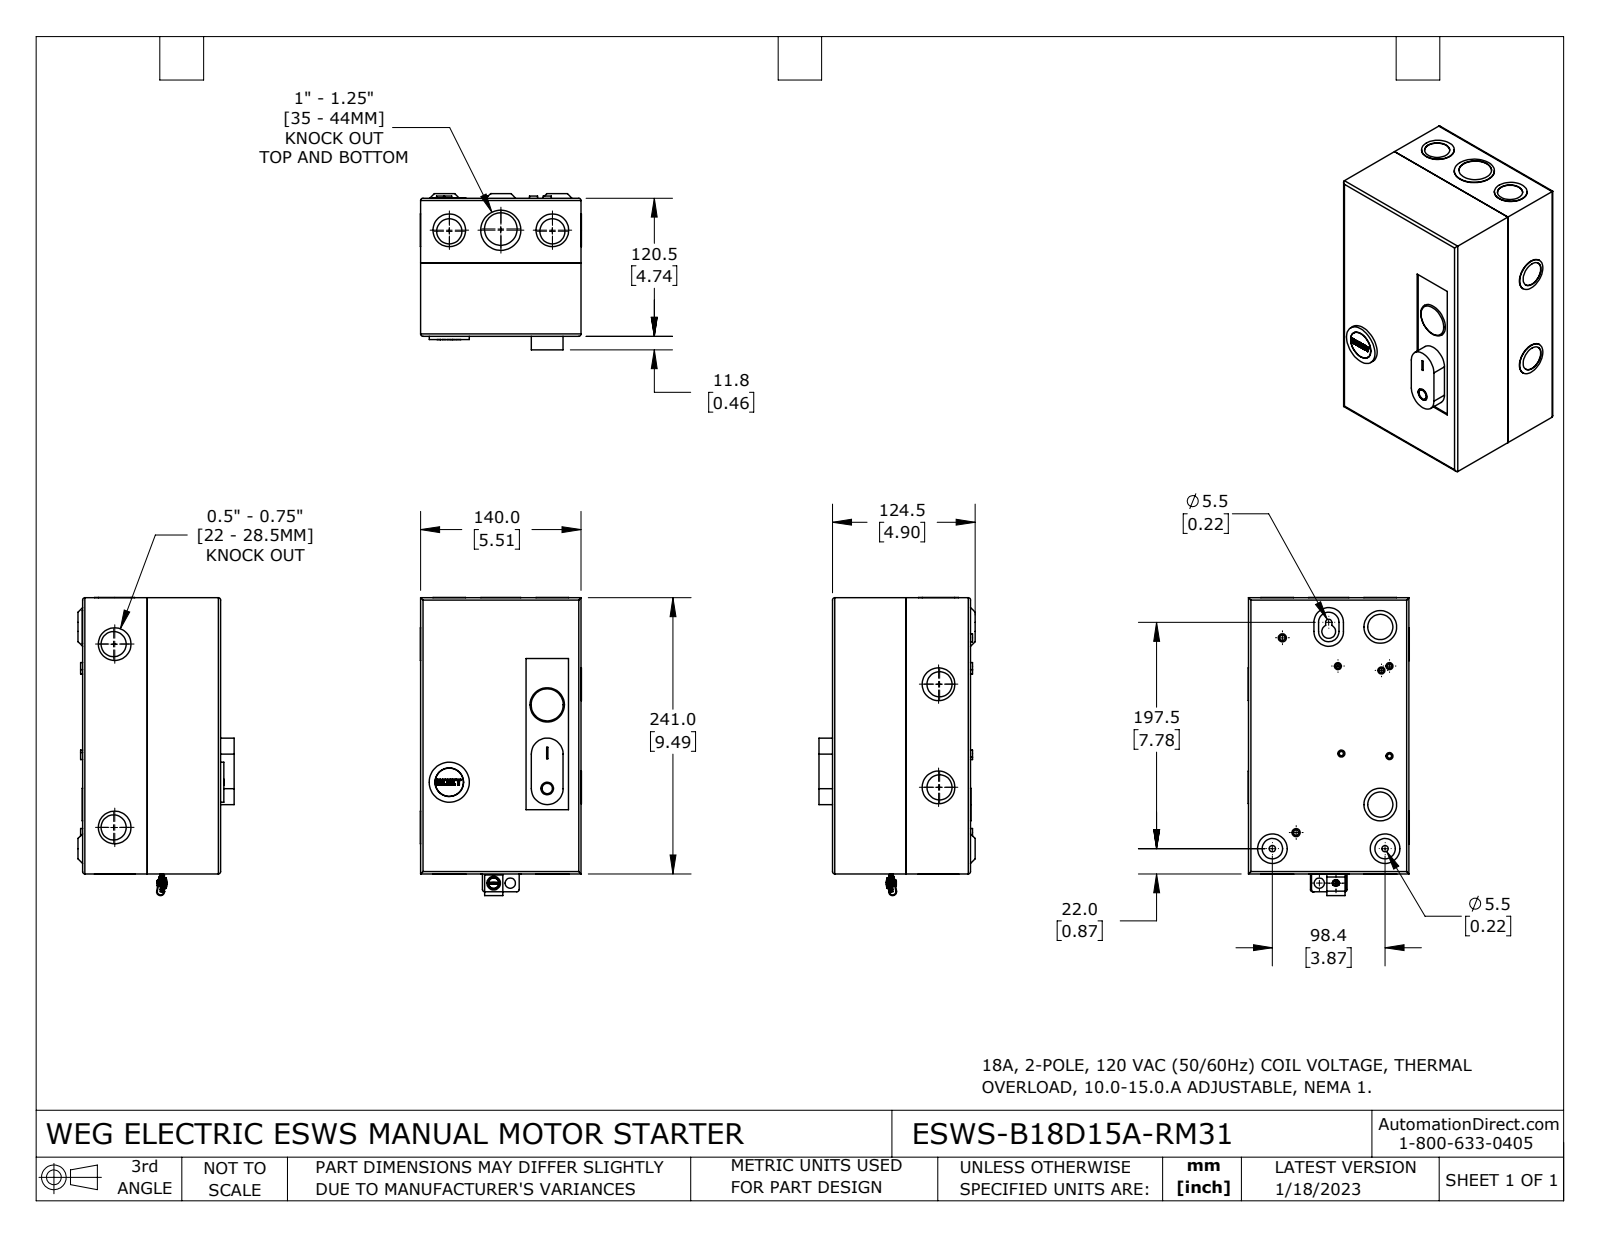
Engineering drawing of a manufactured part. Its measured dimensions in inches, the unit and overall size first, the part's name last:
Units: inches
Overall size (bounding box): 10.248 × 5.535 × 5.366
Round holes (diameter × count): ⌀0.146 ×5, ⌀0.864 ×4, ⌀0.183 ×2, ⌀0.217 ×2, ⌀0.354 ×2, ⌀0.864 ×2, ⌀0.866 ×2, ⌀0.886 ×2, ⌀0.256 ×1, ⌀0.303 ×1, ⌀0.433 ×1, ⌀0.469 ×1
Round bosses / shafts (diameter × count): ⌀1.124 ×6, ⌀0.24 ×5, ⌀1.122 ×2, ⌀0.278 ×2, ⌀1.38 ×1, ⌀1.378 ×1, ⌀1.193 ×1, ⌀1.148 ×1
Partial cylindrical surfaces — rounded edges, fillets, slot ends (radius × count): R0.004 ×34, R0.079 ×13, R0.031 ×4, R0.108 ×3, R0.059 ×2, R0.075 ×2, R0.122 ×2, R0.138 ×2
Main face-to-face distances: 0.047, 4.697, 5.465, 4.65, 9.441, 4.744, 5.417, 5.512, 0.071, 0.063
Hole centre spacings: 0.571, 1.378, 1.773, 3.387, 3.543, 4.921, 5.995, 7.484
Volume: 16.23 in³ · Surface area: 585.2 in²
Bodies: 7 solids, 435 faces (168 planar, 230 cylindrical, 37 other)
Part name (STEP PRODUCT): ESWS-B18D15A-RM31
STEP written by: SolidWorks 2021 (CONFIG_CONTROL_DESIGN)
